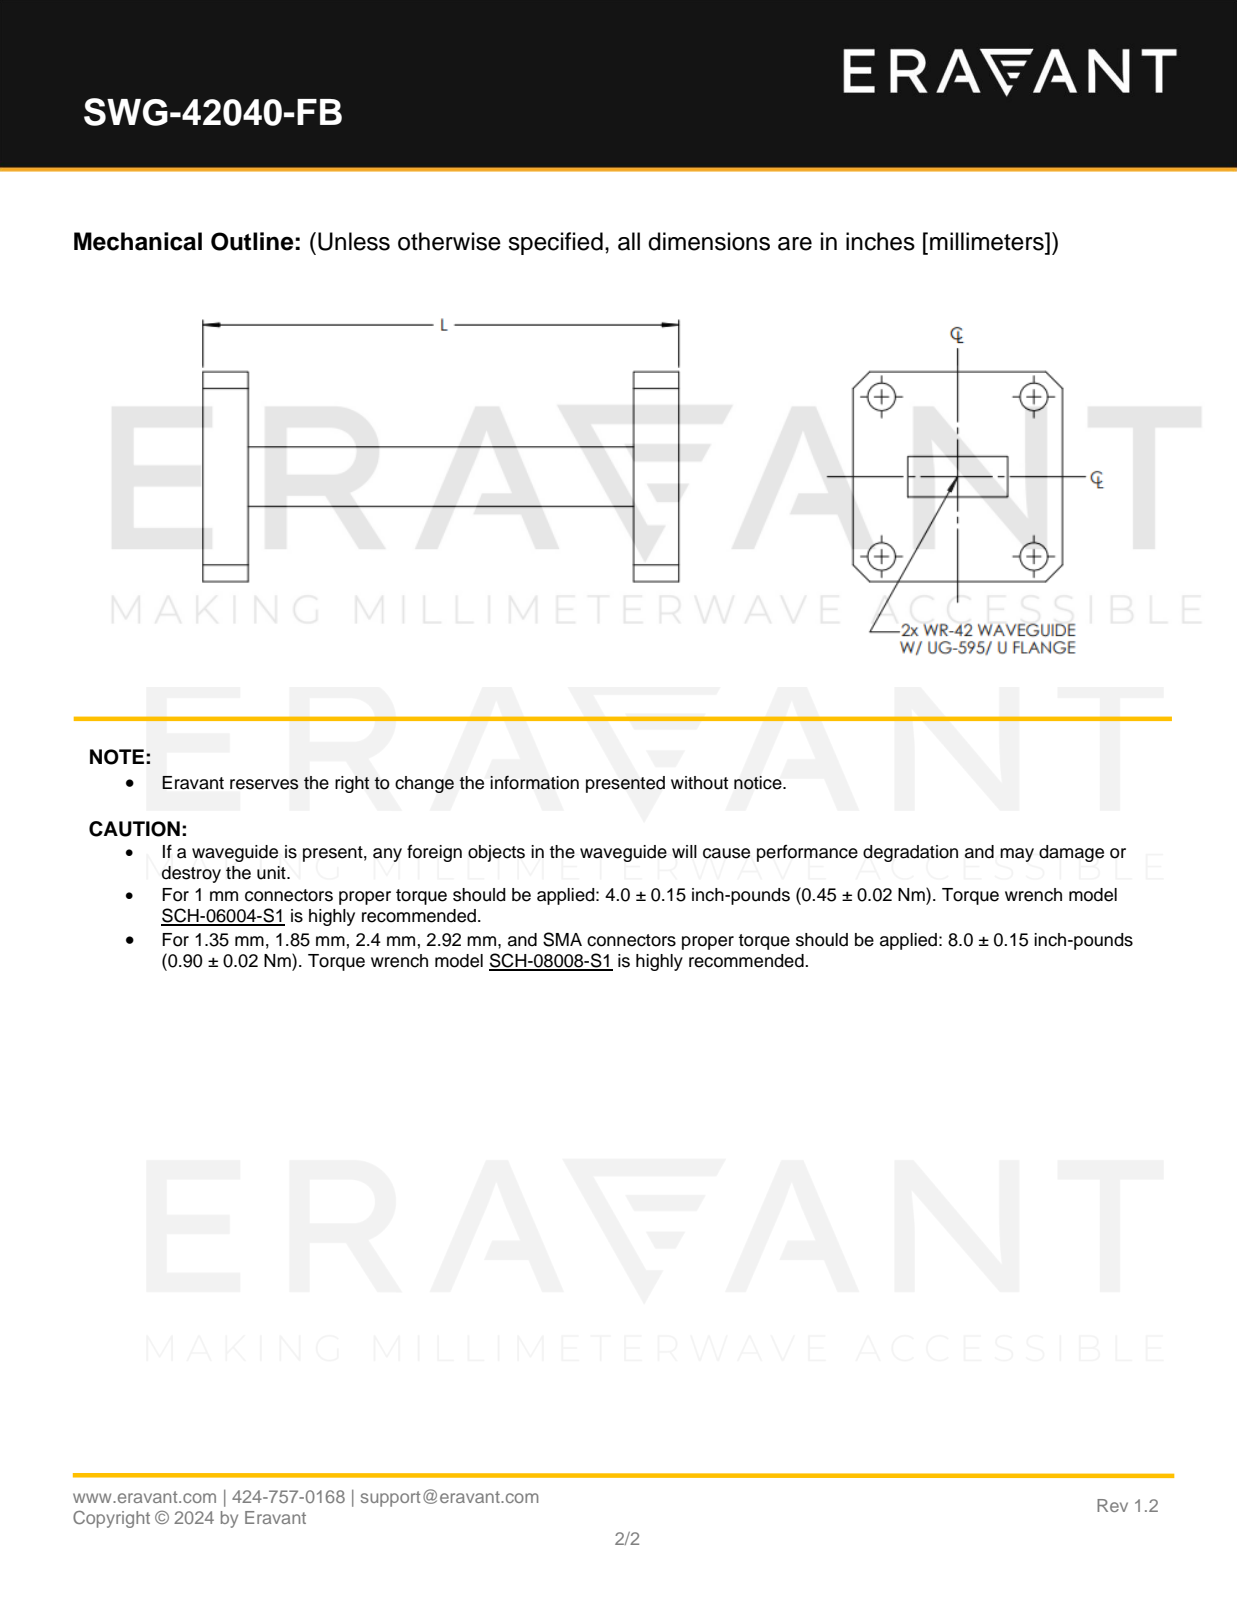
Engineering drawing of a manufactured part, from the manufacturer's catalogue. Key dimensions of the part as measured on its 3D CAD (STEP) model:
Part name (STEP PRODUCT): SWG-42040-FB
STEP written by: SolidWorks 2021 (CONFIG_CONTROL_DESIGN)
Units: inches
Bodies: 1 solid, 50 faces (34 planar, 16 cylindrical, 0 other)
Overall size (bounding box): 4 × 0.88 × 0.88
Volume: 0.726 in³ · Surface area: 9.922 in²
Round holes (diameter × count): ⌀0.116 ×4
Main face-to-face distances: 0.25, 0.19, 3.81, 0.5, 4, 3.62, 0.69, 0.315, 0.565, 0.88
Hole centre spacings: 0.64, 0.67, 0.927
